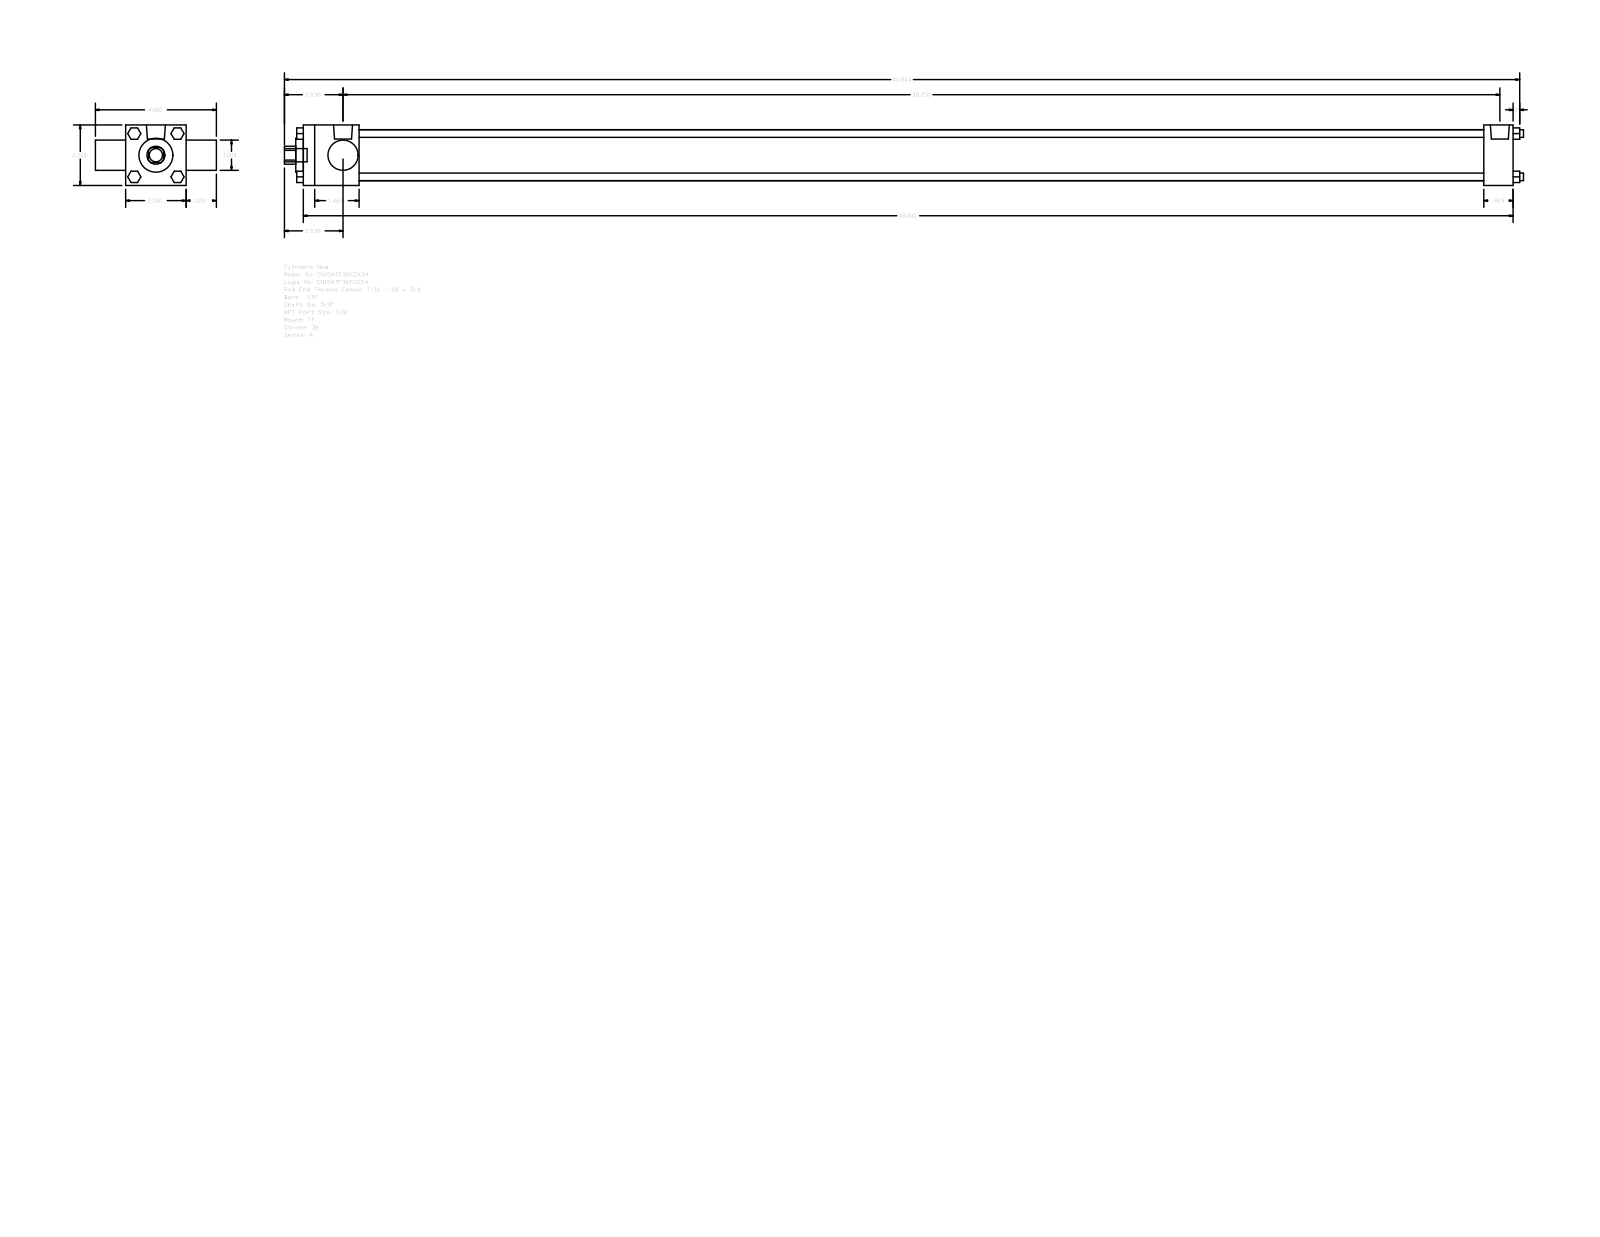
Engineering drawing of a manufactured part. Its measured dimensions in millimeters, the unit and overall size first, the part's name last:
Units: millimetres
Overall size (bounding box): 1040.61 × 101.6 × 50.8
Round holes (diameter × count): ⌀15.88 ×1, ⌀25.4 ×1, ⌀28.57 ×1, ⌀42.93 ×1
Round bosses / shafts (diameter × count): ⌀6.35 ×4, ⌀5.56 ×3, ⌀15.93 ×2, ⌀11.11 ×1
Partial cylindrical surfaces — rounded edges, fillets, slot ends (radius × count): R7.54 ×1
Main face-to-face distances: 50.8, 1016, 25.4, 76.2, 46.83, 991.39, 944.56, 969.17, 24.61, 9.52
Bodies: 0 solids, 120 faces (92 planar, 28 cylindrical, 0 other)
Part name (STEP PRODUCT): A_TF__0150_0.625
STEP written by: GSSL Pune (CONFIG_CONTROL_DESIGN)
